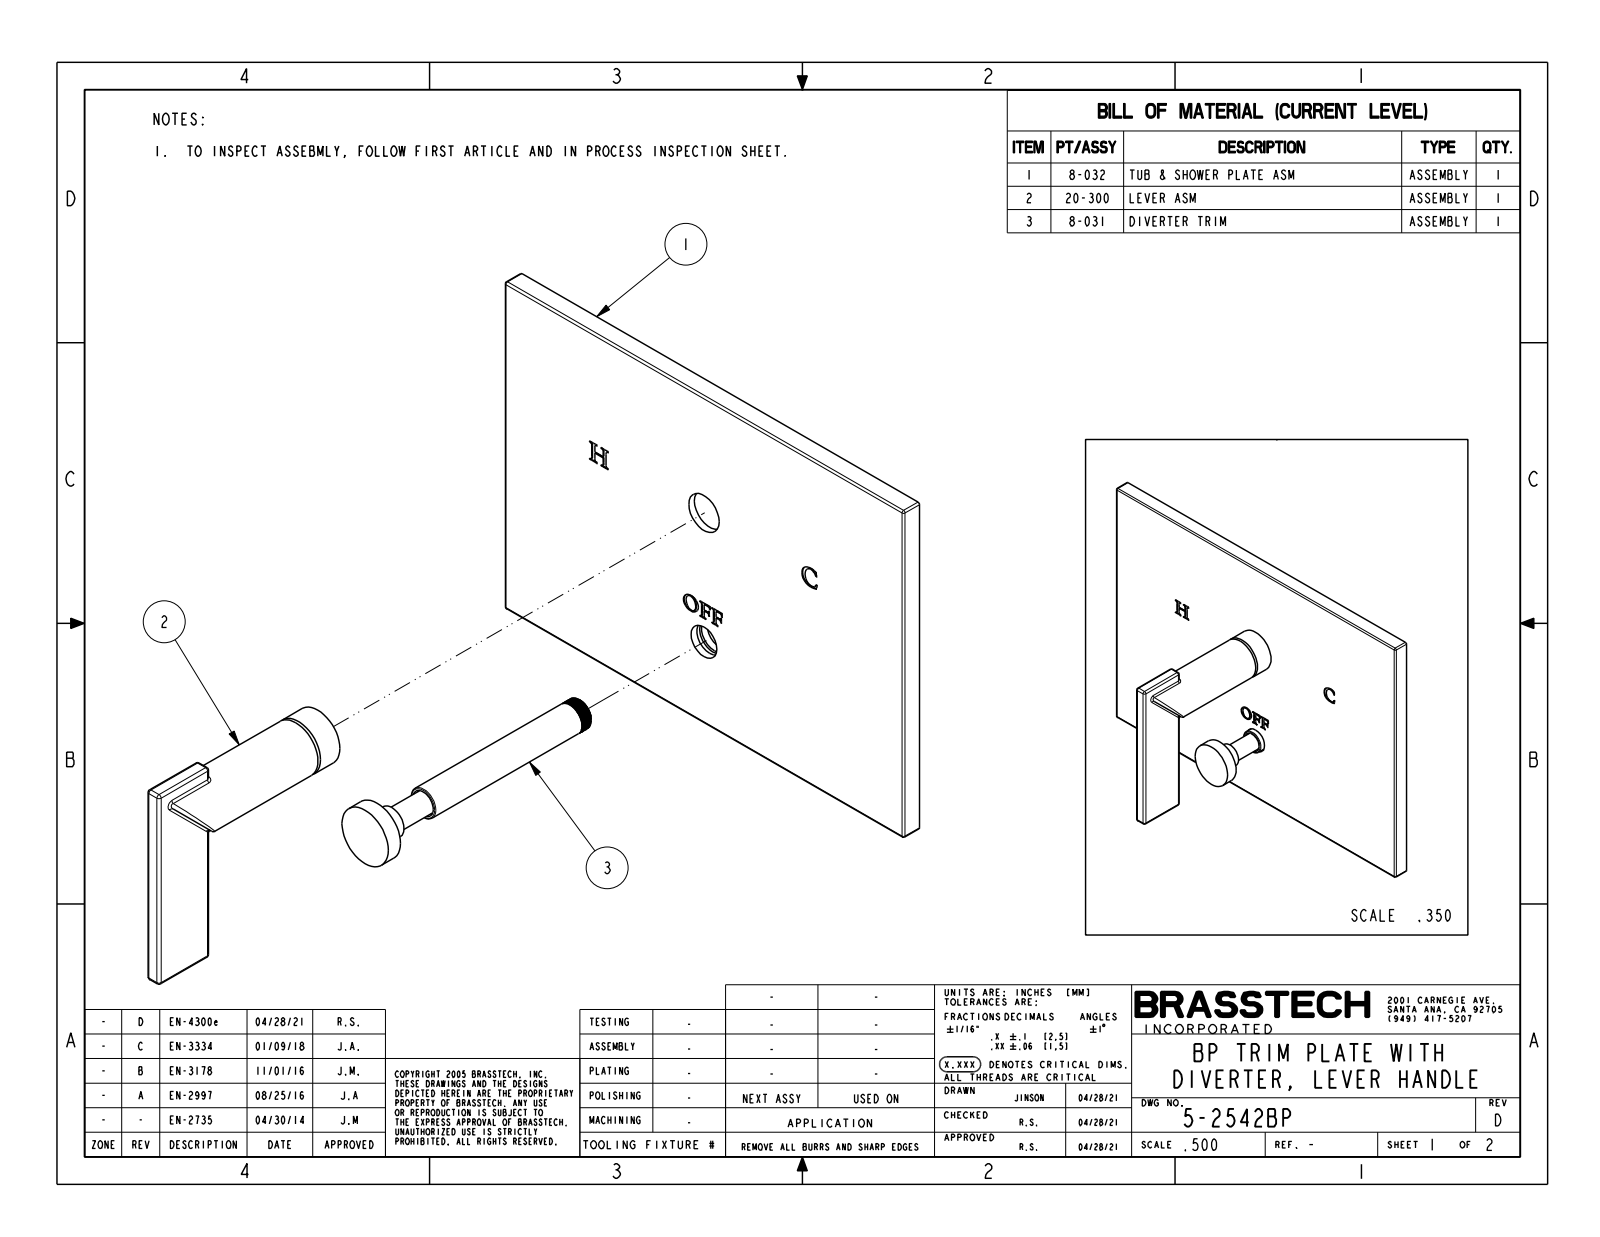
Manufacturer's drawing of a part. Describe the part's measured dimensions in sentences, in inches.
The part is named "5-2542BP". Its 3-D file was written by "CREO PARAMETRIC BY PTC INC, 2018400 (CONFIG_CONTROL_DESIGN)". It is 1 solid with 333 faces: 64 planar, 44 cylindrical and 225 other. Overall it measures 7.75 by 5.5 by 3.51 inches. Its volume is 15.63 cubic inches and its surface area 111.3 square inches. Round holes: 1 of diameter 0.345. Round bosses or shafts: 1 of diameter 0.9, 1 of diameter 0.86, 1 of diameter 0.68, 1 of diameter 0.475, 1 of diameter 0.375, 1 of diameter 0.354, 1 of diameter 0.341. Partial cylindrical surfaces (rounded edges, fillets, slot ends): 16 of radius 0.04, 8 of radius 0.03. The main face-to-face distances are 0.31, 3.757, 3.993, 0.236, 5.5, 7.75, 1.535, 1.225, 3.51, 3.2.
